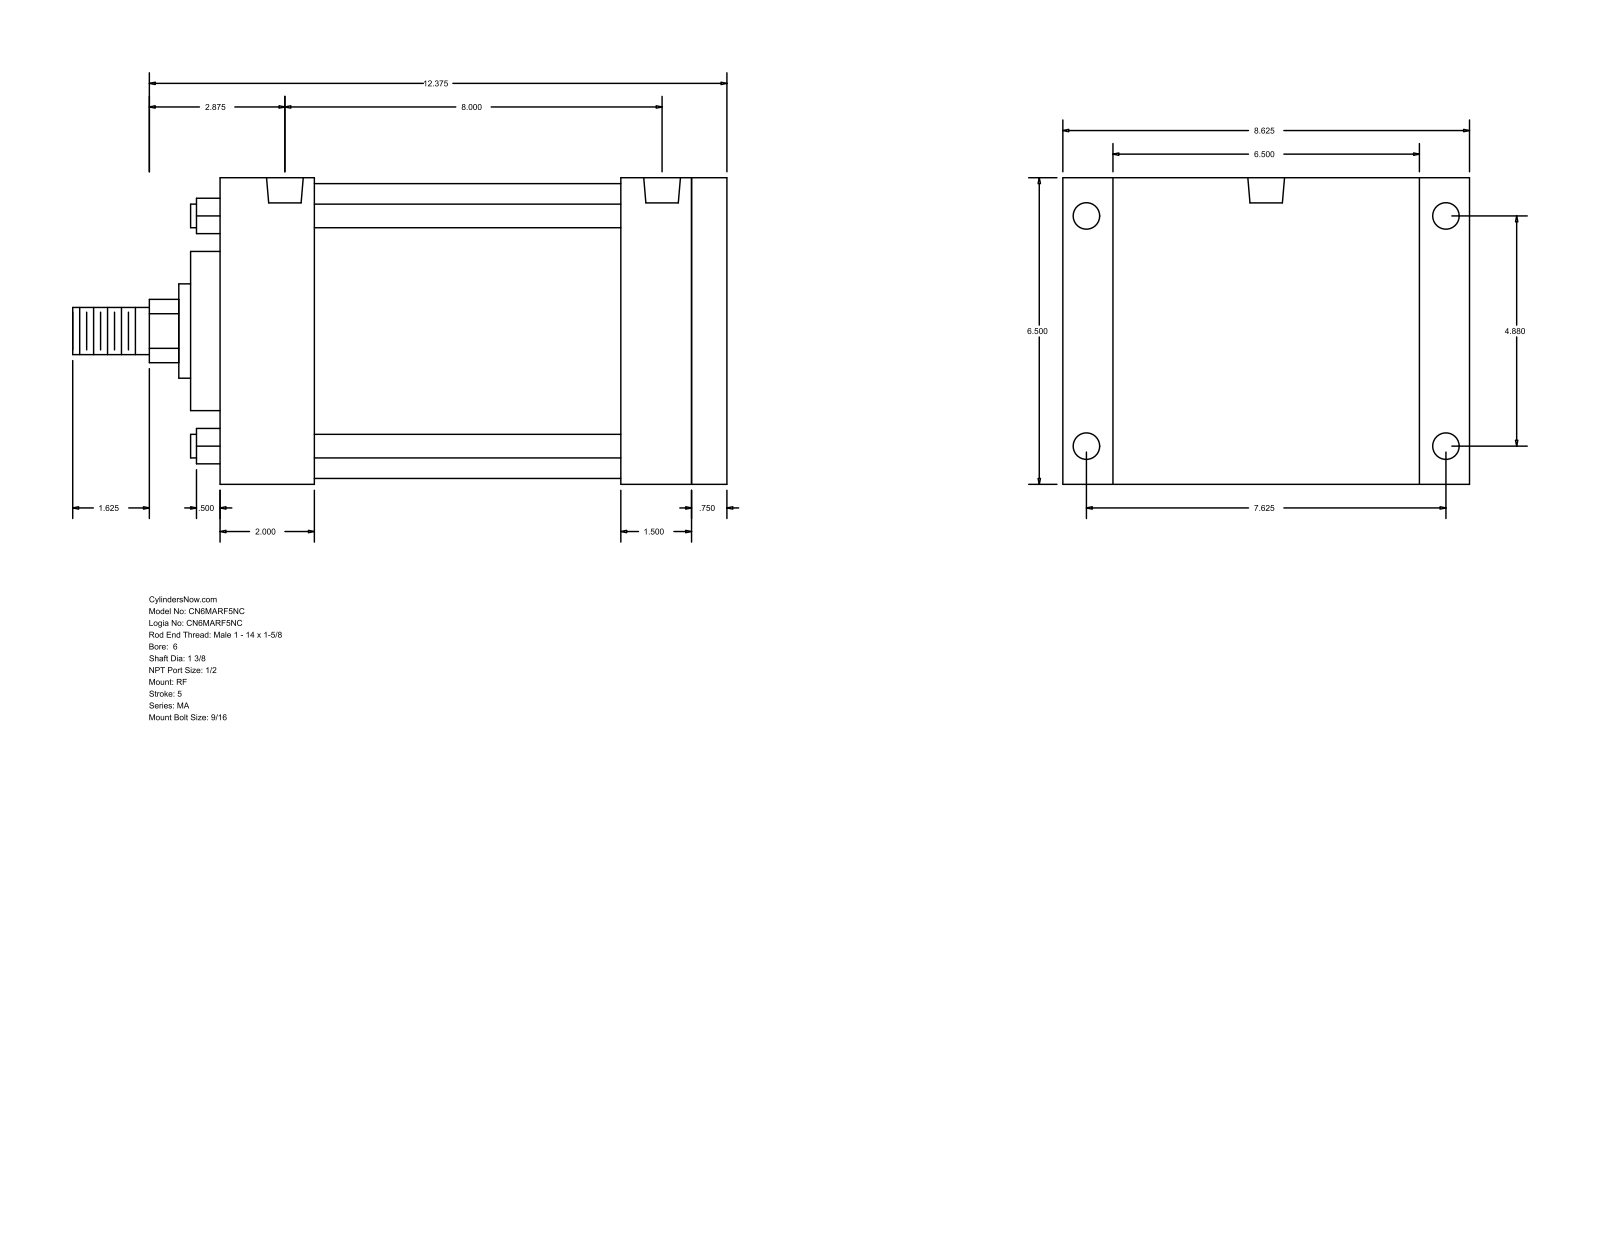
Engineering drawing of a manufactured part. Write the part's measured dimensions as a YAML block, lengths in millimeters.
part_name: "MA_RF__0600_1.375"
step_written_by: "GSSL Pune (CONFIG_CONTROL_DESIGN)"
units: millimeters
bodies: {solids: 0, faces: 94, planar: 65, cylindrical: 29, other: 0}
overall_size: [355.6, 219.07, 165.1]
round_holes:
  - {diameter: 14.29, count: 4}
  - {diameter: 17.46, count: 4}
  - {diameter: 19.77, count: 2}
round_bosses_or_shafts:
  - {diameter: 12.7, count: 4}
  - {diameter: 158.75, count: 1}
  - {diameter: 85.72, count: 1}
  - {diameter: 50.8, count: 1}
  - {diameter: 34.92, count: 1}
  - {diameter: 25.4, count: 1}
partial_cylinders:
  - {radius: 17.06, count: 1}
face_to_face_distances: [165.1, 276.22, 219.08, 19.05, 257.17, 50.8, 206.37, 225.42, 168.28, 38.09]
hole_center_spacings: [123.96, 193.68, 206.38, 229.95, 3.18, 203.2]
